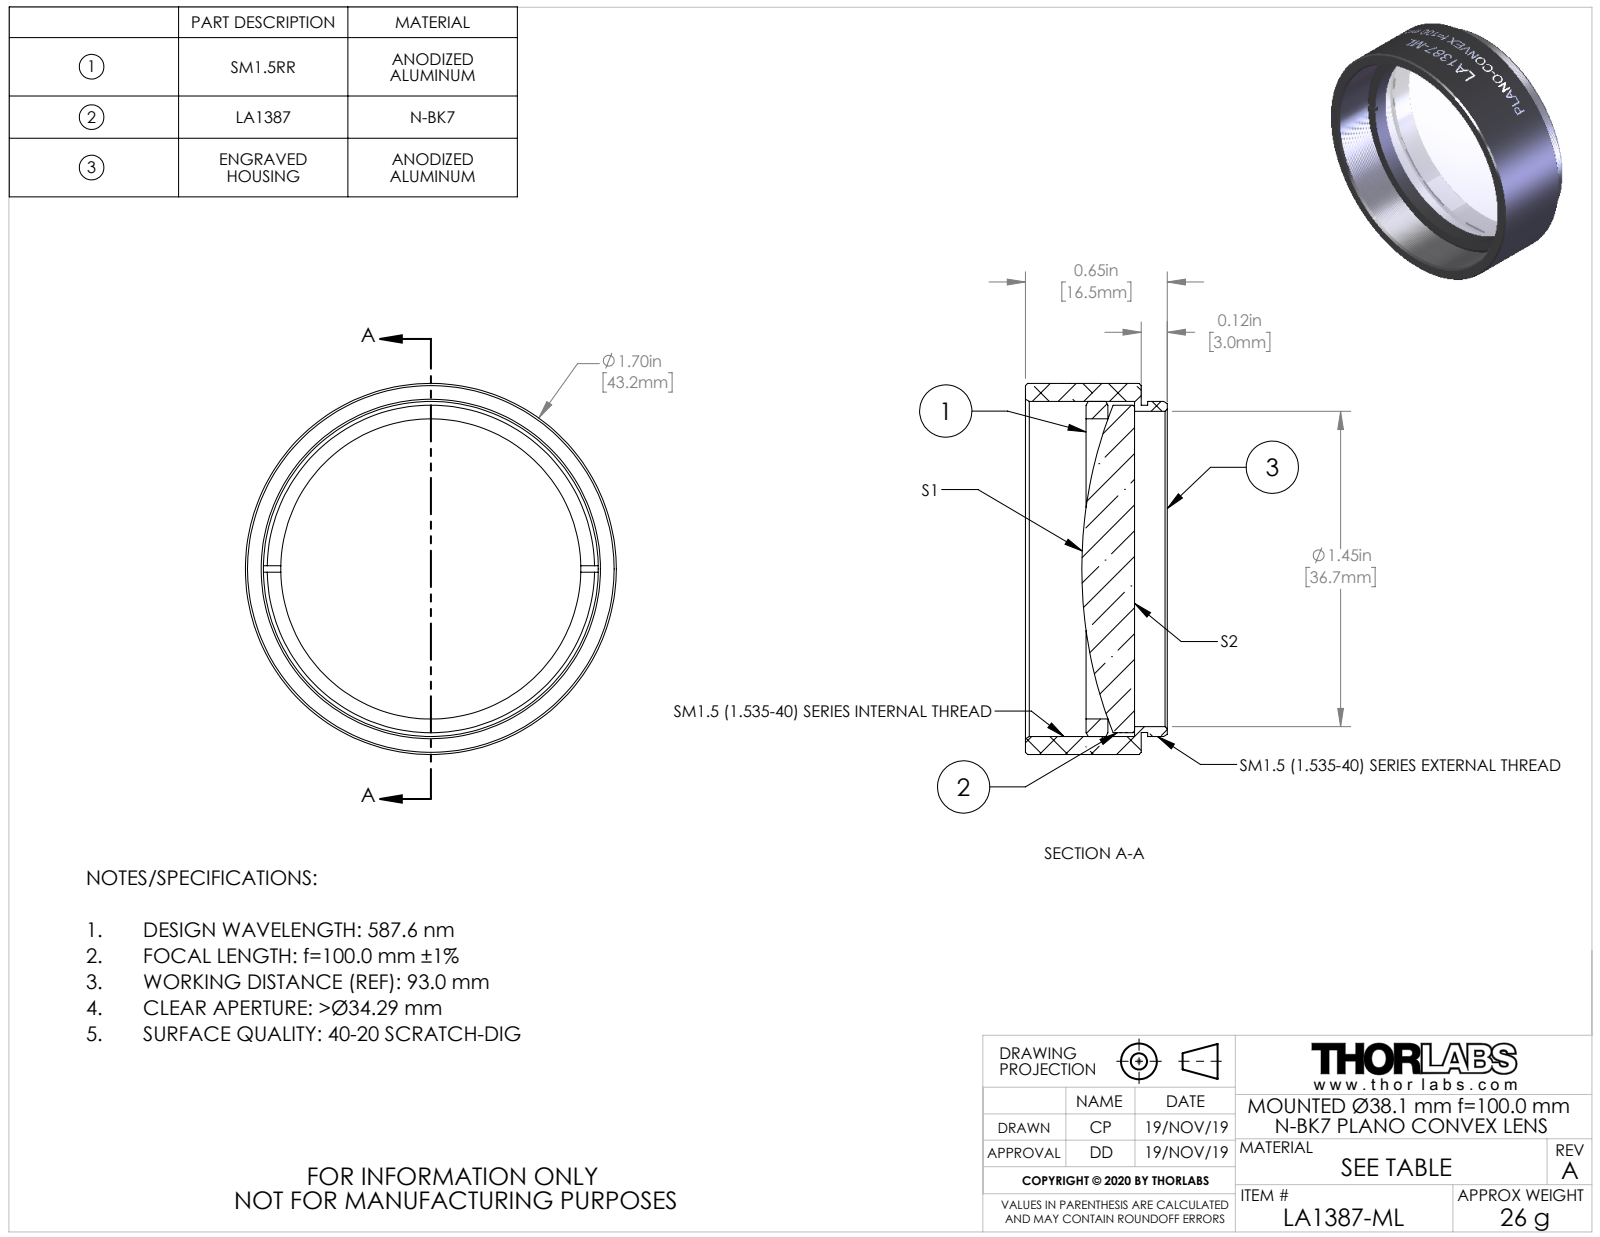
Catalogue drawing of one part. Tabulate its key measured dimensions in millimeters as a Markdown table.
| quantity | value |
| --- | --- |
| part name | TTN200689-E0W |
| STEP written by | SolidWorks 2018 (CONFIG_CONTROL_DESIGN) |
| units | millimeters |
| bodies | 3 solids, 120 faces (15 planar, 86 cylindrical, 19 other) |
| overall size | 43.18 × 43.18 × 16.51 |
| volume | 9 623 mm³ |
| surface area | 8 639 mm² |
| round holes (diameter × count) | 34.92 × 1, 36.7 × 1 |
| round bosses / shafts (diameter × count) | 43.18 × 1, 38.99 × 1, 38.1 × 1, 38.07 × 1 |
| main face-to-face distances | 0.76, 13.46, 12.7, 3.86, 3.1, 9.6, 6.4, 5.64, 2.54, 7.06 |
